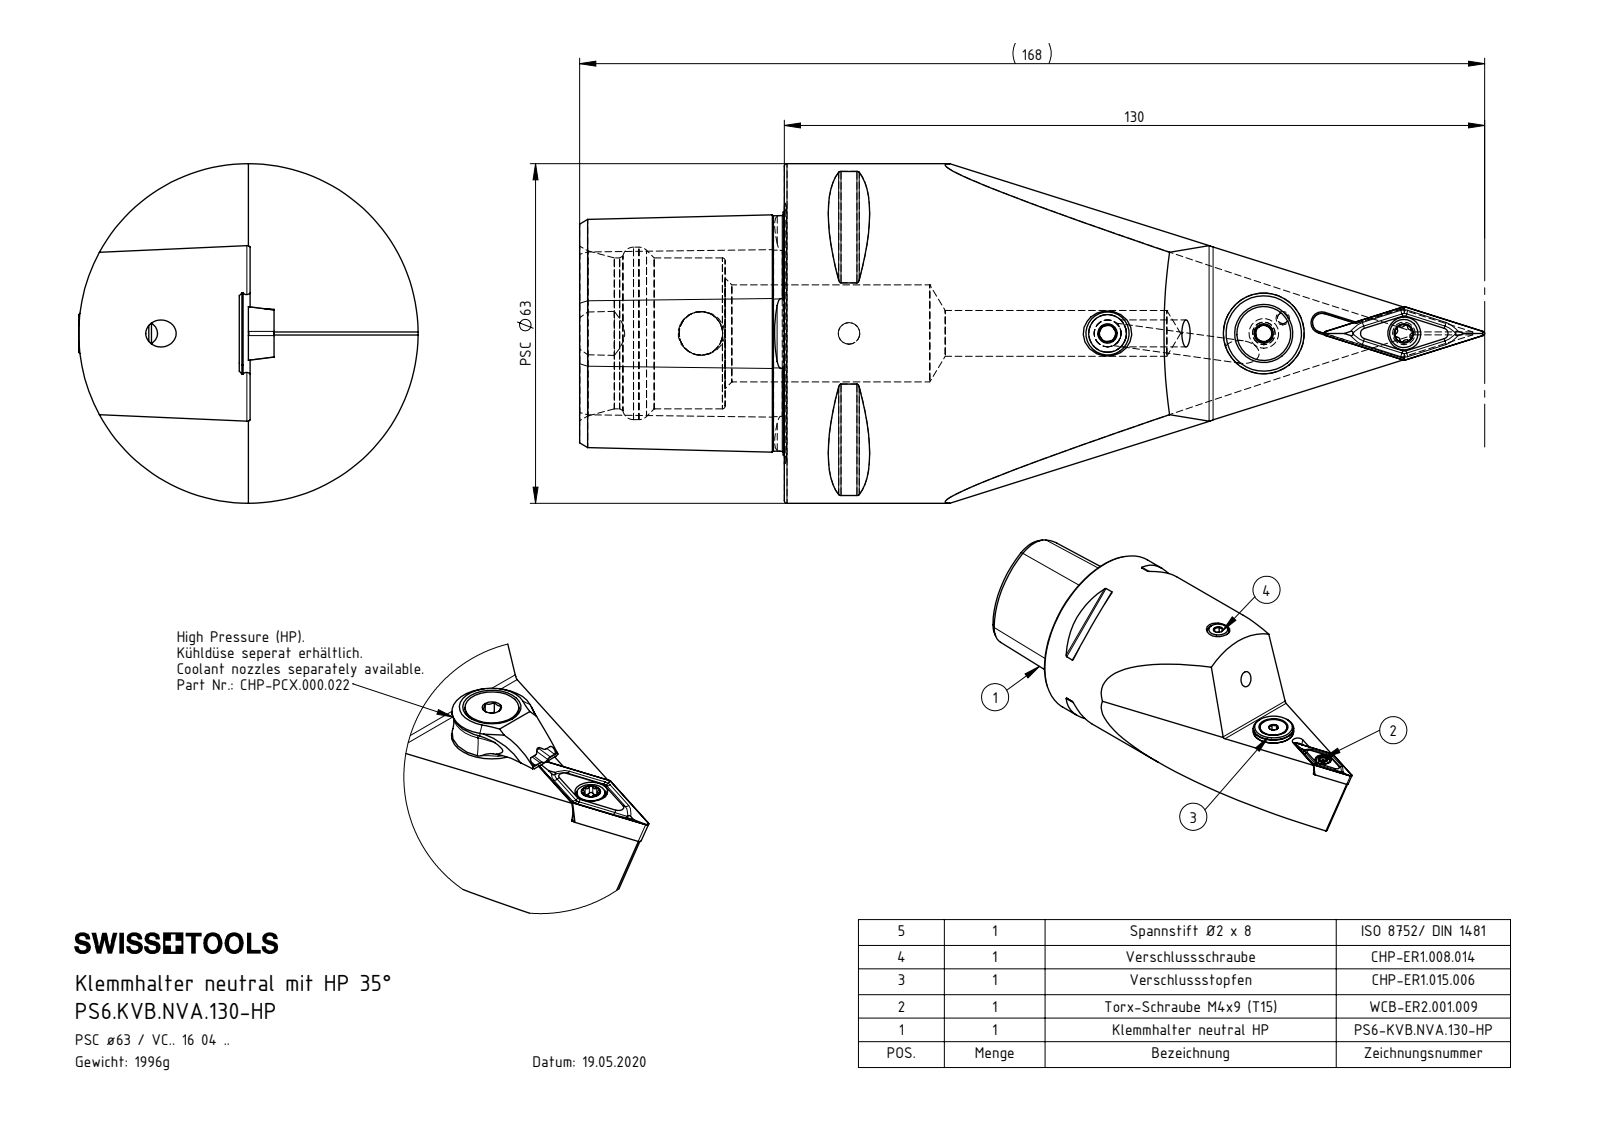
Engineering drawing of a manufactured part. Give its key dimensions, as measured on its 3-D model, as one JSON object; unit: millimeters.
{"part_name": "CHP-ER1.015.006_A; PS6.KVB.NVA.130-HP; WCB-ER2.001.009_A; DIN 3771 - 13x1 (+6 more)", "step_written_by": "SolidWorks 2017 (AUTOMOTIVE_DESIGN)", "units": "millimeters", "bodies": {"solids": 8, "faces": 277, "planar": 93, "cylindrical": 63, "other": 121}, "overall_size": [168, 63, 63], "volume_mm3": 276826, "surface_area_mm2": 39320, "round_holes": [[4.2, 2], [5, 2], [1.2, 1], [2, 1], [2.5, 1], [3, 1], [3.3, 1], [4, 1], [4.4, 1], [5.2, 1], [6.1, 1], [7, 1]], "round_bosses_or_shafts": [[63, 1], [15, 1], [13.4, 1], [10, 1], [8, 1], [5.5, 1], [5.25, 1], [5, 1]], "partial_cylinders_radius": [[0.5, 10], [0.34, 6], [0.59, 6], [0.8, 2], [1.75, 1], [6, 1], [7, 1]], "face_to_face_distances": [38, 24.88, 4.5, 27, 11, 4.46, 55.8, 37.8, 10.8, 6.4], "hole_center_spacings": [4.5, 20.09, 21.59, 21.69, 23.76, 24.9, 25, 27.5]}
